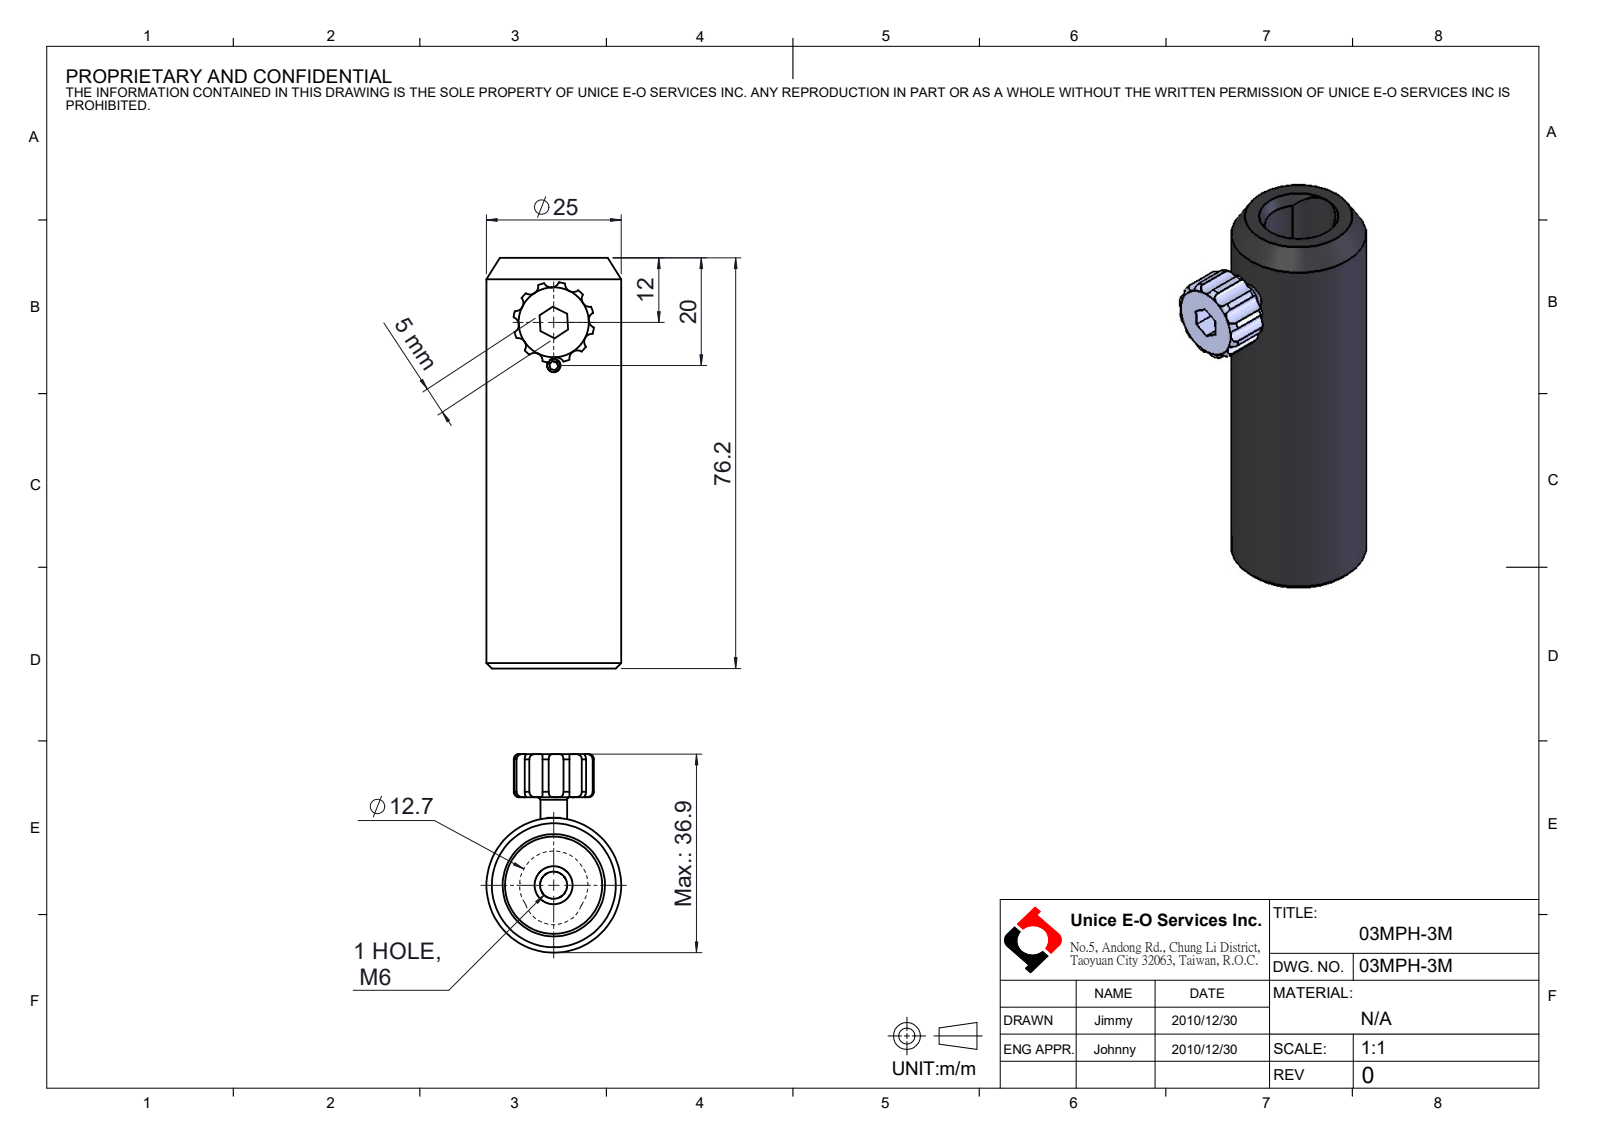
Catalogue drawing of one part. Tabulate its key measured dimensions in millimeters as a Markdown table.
| quantity | value |
| --- | --- |
| part name | 03MPH-3M |
| STEP written by | SolidWorks 2016 (CONFIG_CONTROL_DESIGN) |
| units | millimeters |
| bodies | 6 solids, 127 faces (25 planar, 50 cylindrical, 52 other) |
| overall size | 76.2 × 36.85 × 25 |
| volume | 28 752 mm³ |
| surface area | 11 965 mm² |
| round holes (diameter × count) | 5 × 2, 2.3 × 1, 2.5 × 1, 19 × 1 |
| round bosses / shafts (diameter × count) | 25 × 1, 4.94 × 1, 3 × 1 |
| partial cylindrical surfaces (radius × count) | 1.5 × 12, 5.5 × 1, 6.35 × 1, 7.5 × 1 |
| main face-to-face distances | 8, 76.2, 68.2, 5.1, 4.2, 3.8, 1.5, 6.85, 11.05, 14.85 |
| hole center spacings | 8 |
